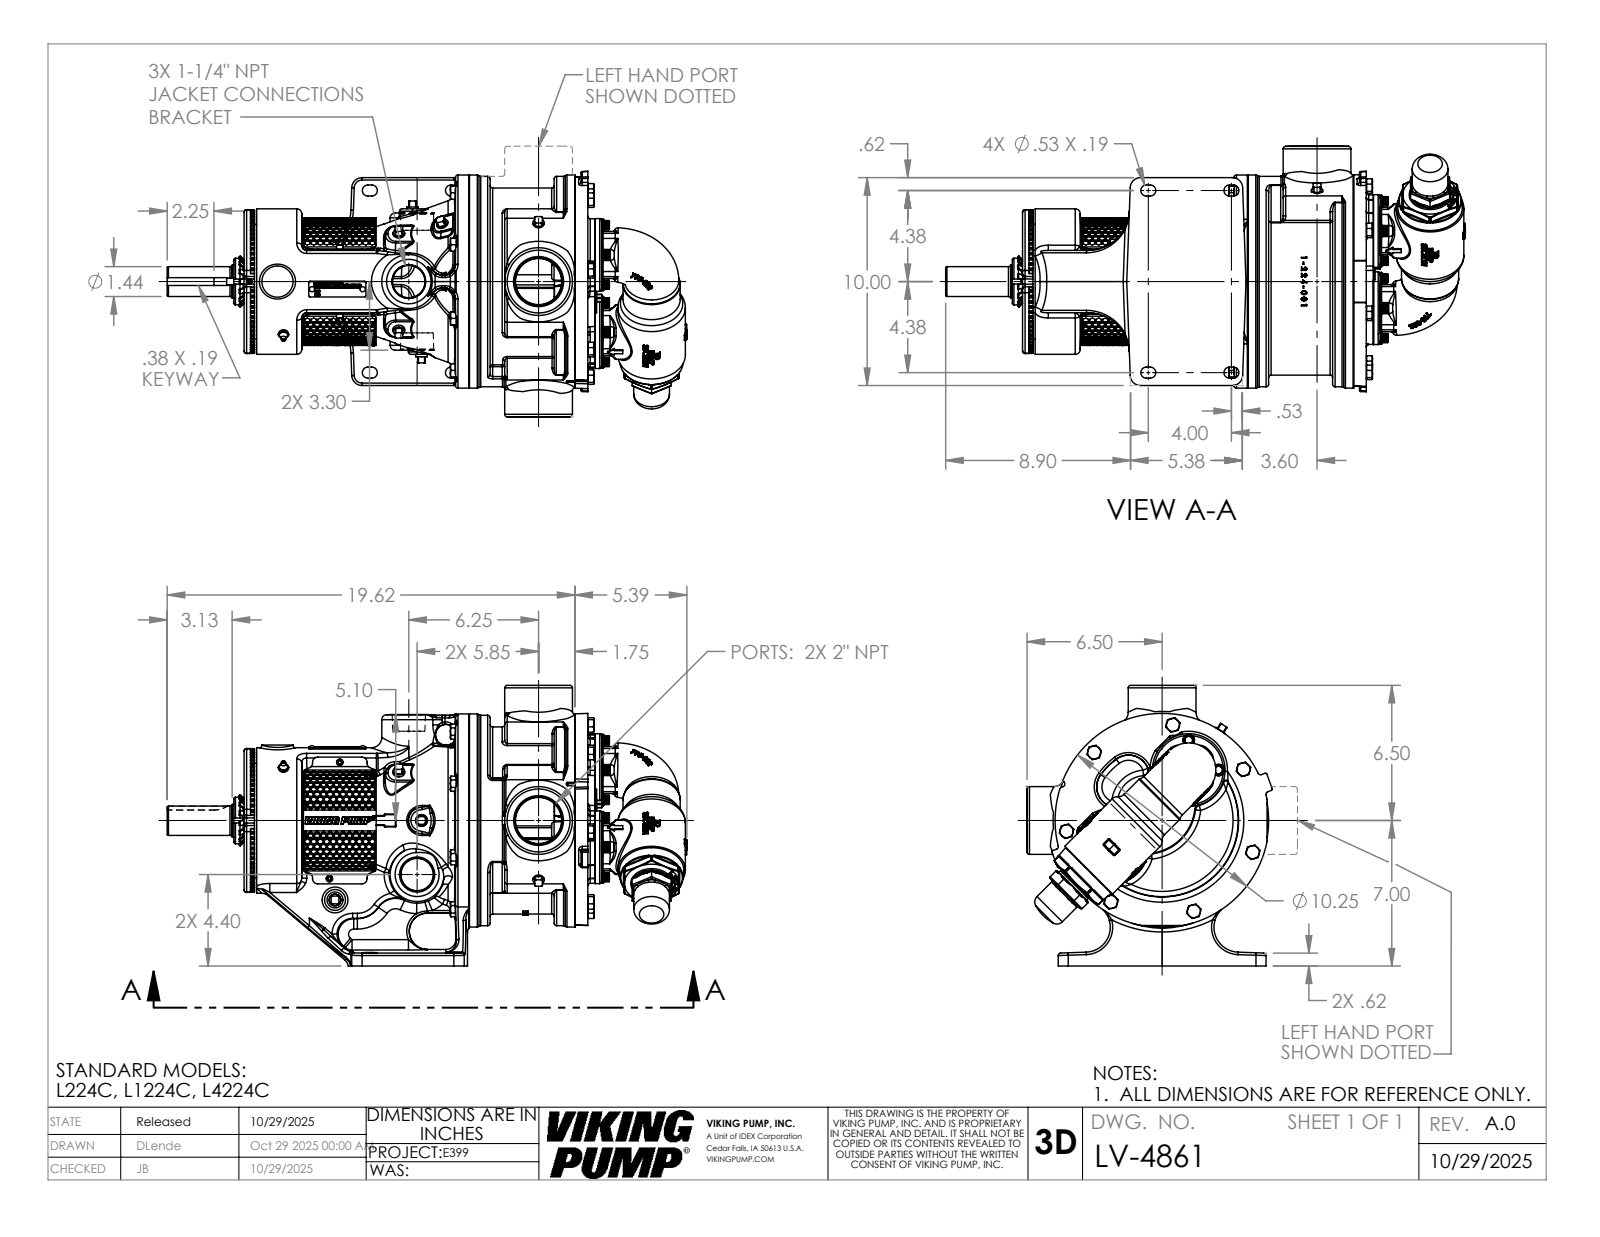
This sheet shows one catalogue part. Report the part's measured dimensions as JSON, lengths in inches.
{"part_name": "LV-4861", "step_written_by": "SolidWorks 2024 (AUTOMOTIVE_DESIGN)", "units": "inches", "bodies": {"solids": 1, "faces": 5276, "planar": 1746, "cylindrical": 1059, "other": 2471}, "overall_size": [25.01, 13.5, 11.817], "volume_in3": 935.3, "surface_area_in2": 1285, "round_holes": [[0.406, 8], [0.41, 8], [1.094, 8], [0.199, 6], [0.25, 6], [0.159, 3], [0.266, 2], [0.313, 2], [0.453, 1], [1.552, 1], [1.577, 1], [1.593, 1]], "round_bosses_or_shafts": [[0.625, 9], [0.563, 8], [0.625, 6], [0.375, 5], [3.5, 3], [0.437, 3], [0.375, 3], [0.312, 3]], "partial_cylinders_radius": [[0.063, 109], [0.069, 74], [0.12, 68], [0.03, 38], [0.5, 26], [0.24, 16], [0.45, 16], [0.06, 13]], "face_to_face_distances": [13.792, 3.537, 10.255, 2.25, 0.5, 2.143, 5.68, 15.935, 0.607, 2.75], "hole_center_spacings": [3, 1.375, 3.609, 1.709, 2.18, 2.249, 4.089, 4.446]}
